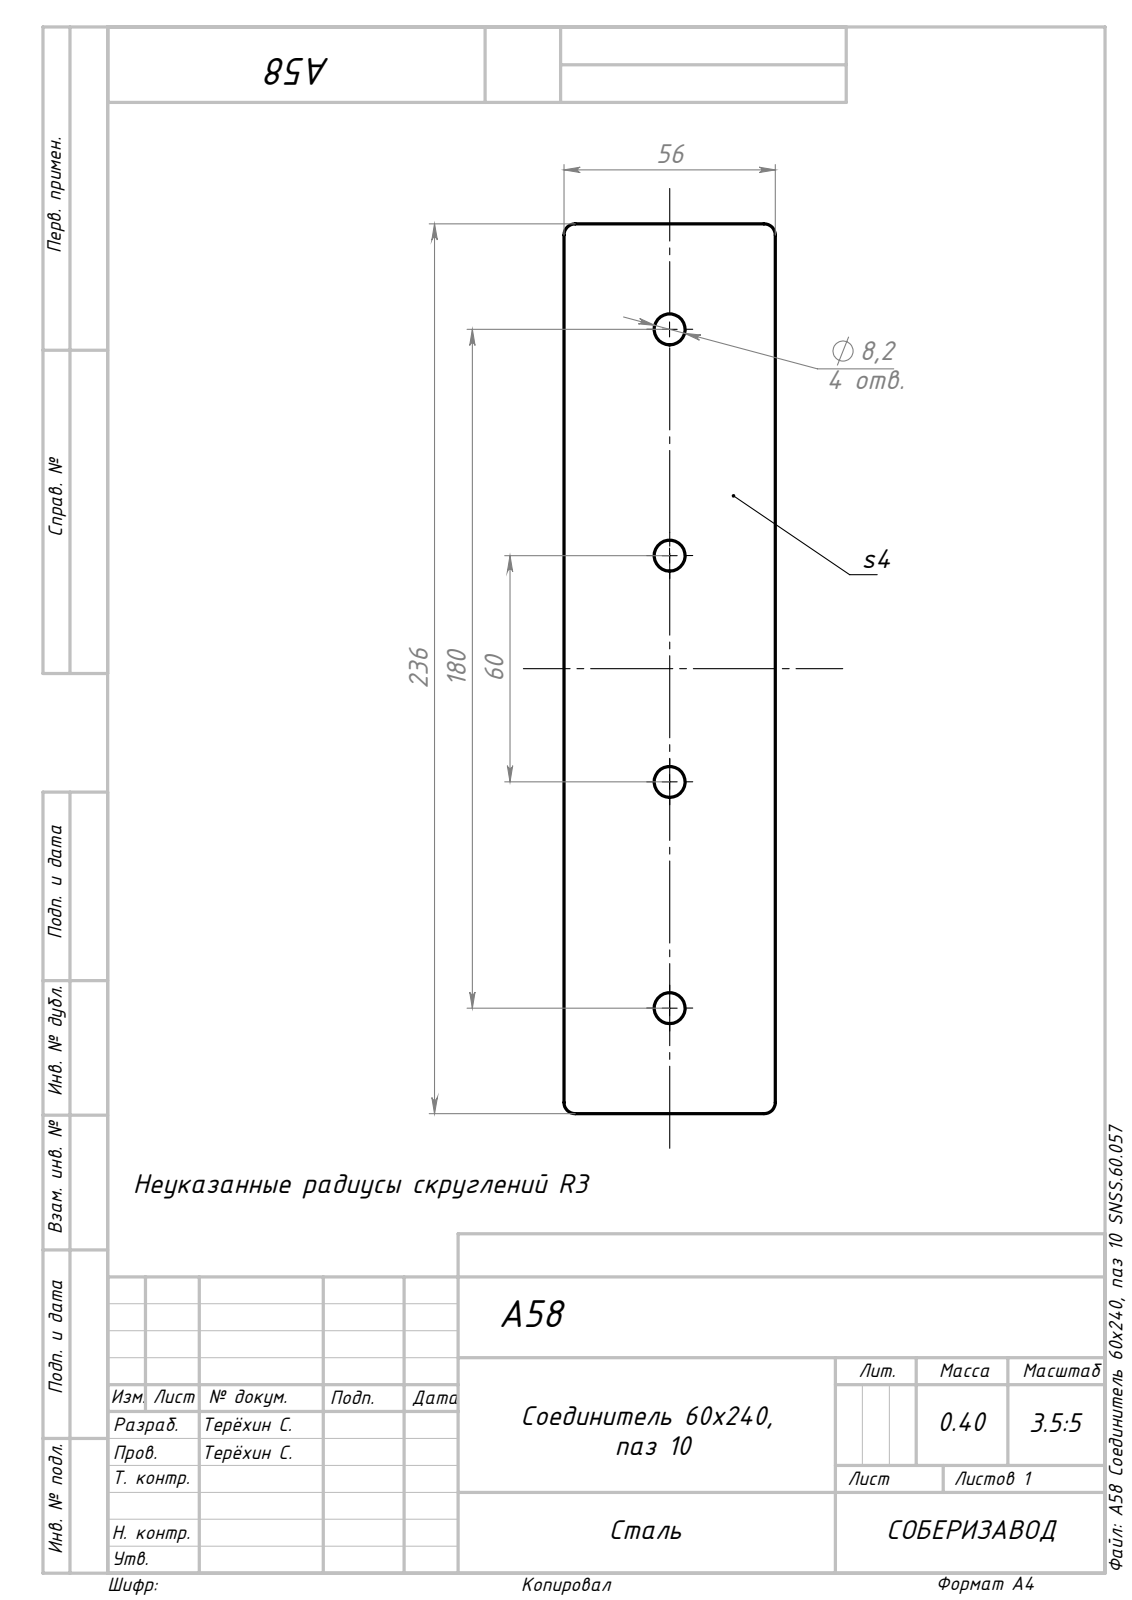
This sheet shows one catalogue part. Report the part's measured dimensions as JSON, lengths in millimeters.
{"part_name": "A58 Cоединитель 60x240, паз 10 SNSS.60.057_00; Сборка1", "step_written_by": "SolidWorks 2022 (AUTOMOTIVE_DESIGN)", "units": "millimeters", "bodies": {"solids": 1, "faces": 18, "planar": 6, "cylindrical": 12, "other": 0}, "overall_size": [236, 56, 4], "volume_mm3": 51988, "surface_area_mm2": 28722, "round_holes": [[8.2, 4]], "partial_cylinders_radius": [[3, 4]], "face_to_face_distances": [4, 56, 236], "hole_center_spacings": [60, 120, 180]}
